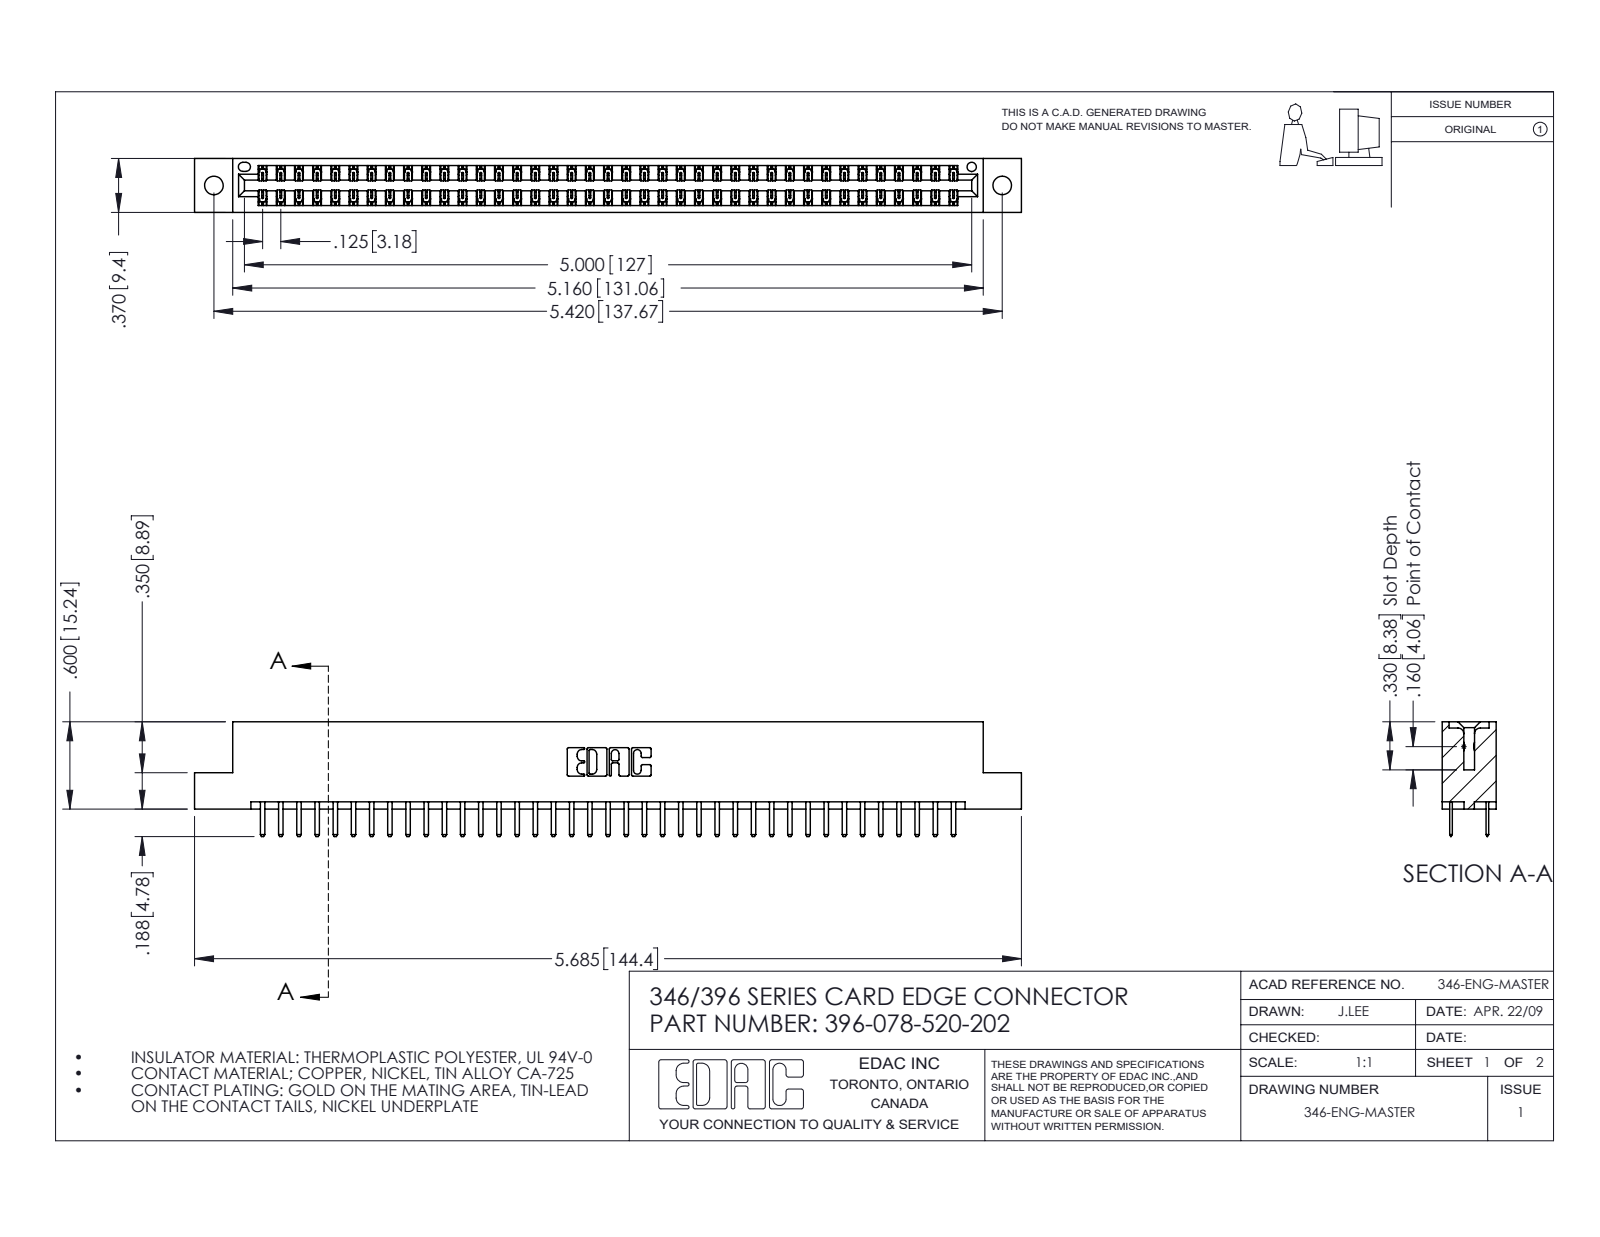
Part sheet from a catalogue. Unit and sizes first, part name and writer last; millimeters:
Units: millimetres
Overall size (bounding box): 144.4 × 20 × 9.4
Round holes (diameter × count): ⌀3.3 ×2, ⌀1.6 ×1
Partial cylindrical surfaces — rounded edges, fillets, slot ends (radius × count): R0.2 ×117, R0.3 ×82, R0.3 ×22, R0.2 ×6, R0.8 ×6, R0.7 ×3, R0.4 ×2, R0.6 ×2
Main face-to-face distances: 1.2, 8.2, 6.4, 9.4, 7, 1.8, 7.6, 0.6, 3.8, 5.6
Hole centre spacings: 6.2, 132.4, 137.7
Volume: 14 000 mm³ · Surface area: 18 830 mm²
Bodies: 79 solids, 4490 faces (2962 planar, 1528 cylindrical, 0 other)
Part name (STEP PRODUCT): 346 Part_Flush Mounting Lugs - 0.128 Dia; 345-292-001_345-293-120; 396-078-520-202
STEP written by: SolidWorks 2016 (CONFIG_CONTROL_DESIGN)
